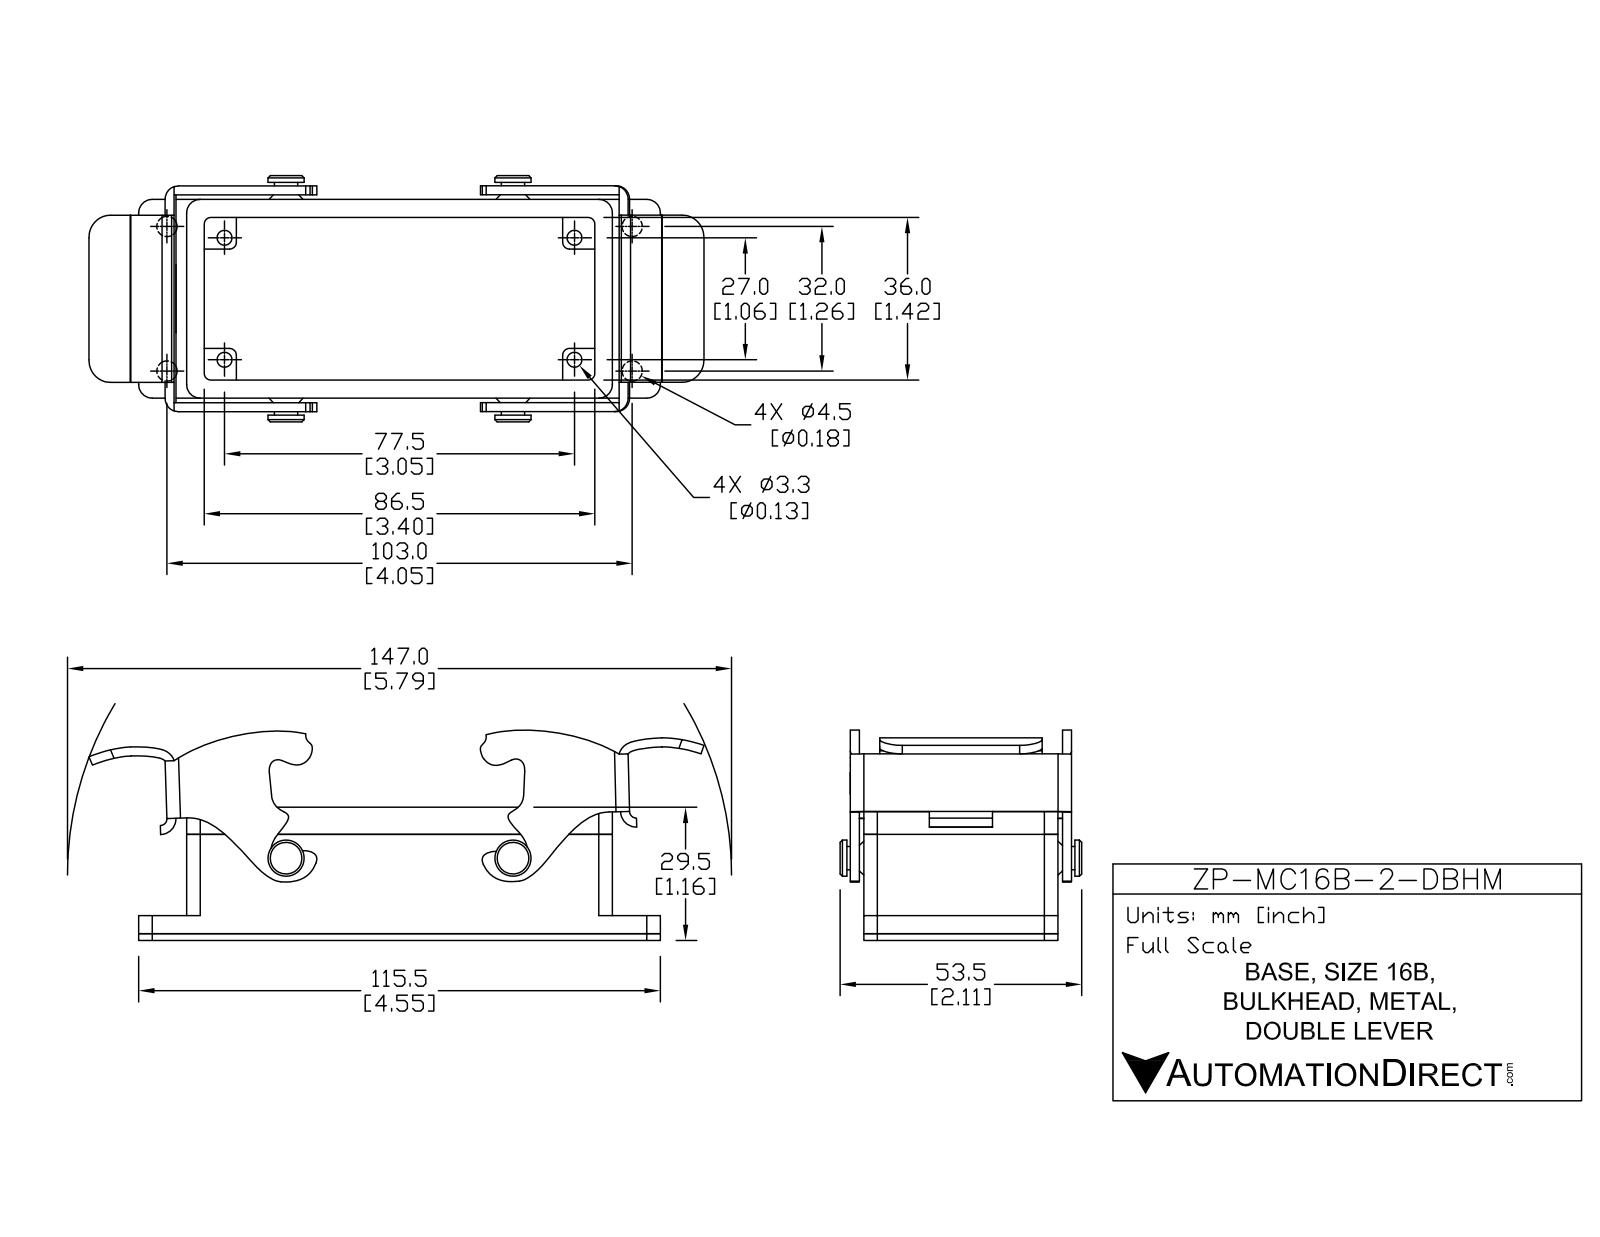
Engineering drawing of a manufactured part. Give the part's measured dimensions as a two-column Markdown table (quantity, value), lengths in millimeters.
| quantity | value |
| --- | --- |
| part name | ZP-MC16B-2-DBHM |
| STEP written by | SolidWorks 2011 (AUTOMOTIVE_DESIGN) |
| units | millimeters |
| bodies | 9 solids, 314 faces (130 planar, 176 cylindrical, 8 other) |
| overall size | 146.76 × 54.5 × 43.67 |
| volume | 39 428 mm³ |
| surface area | 37 703 mm² |
| round holes (diameter × count) | 3.3 × 4, 4.5 × 4 |
| round bosses / shafts (diameter × count) | 8 × 2, 5.17 × 2 |
| partial cylindrical surfaces (radius × count) | 0.5 × 26, 1.5 × 12, 3 × 10, 2 × 6, 4 × 6, 1 × 4, 10 × 4, 2.77 × 3 |
| main face-to-face distances | 1.15, 3, 4, 44, 5.25, 45.25, 41, 40, 1, 37 |
| hole center spacings | 12.99, 32.14, 90.28, 94.95, 27, 32, 77.5, 82.07 |
